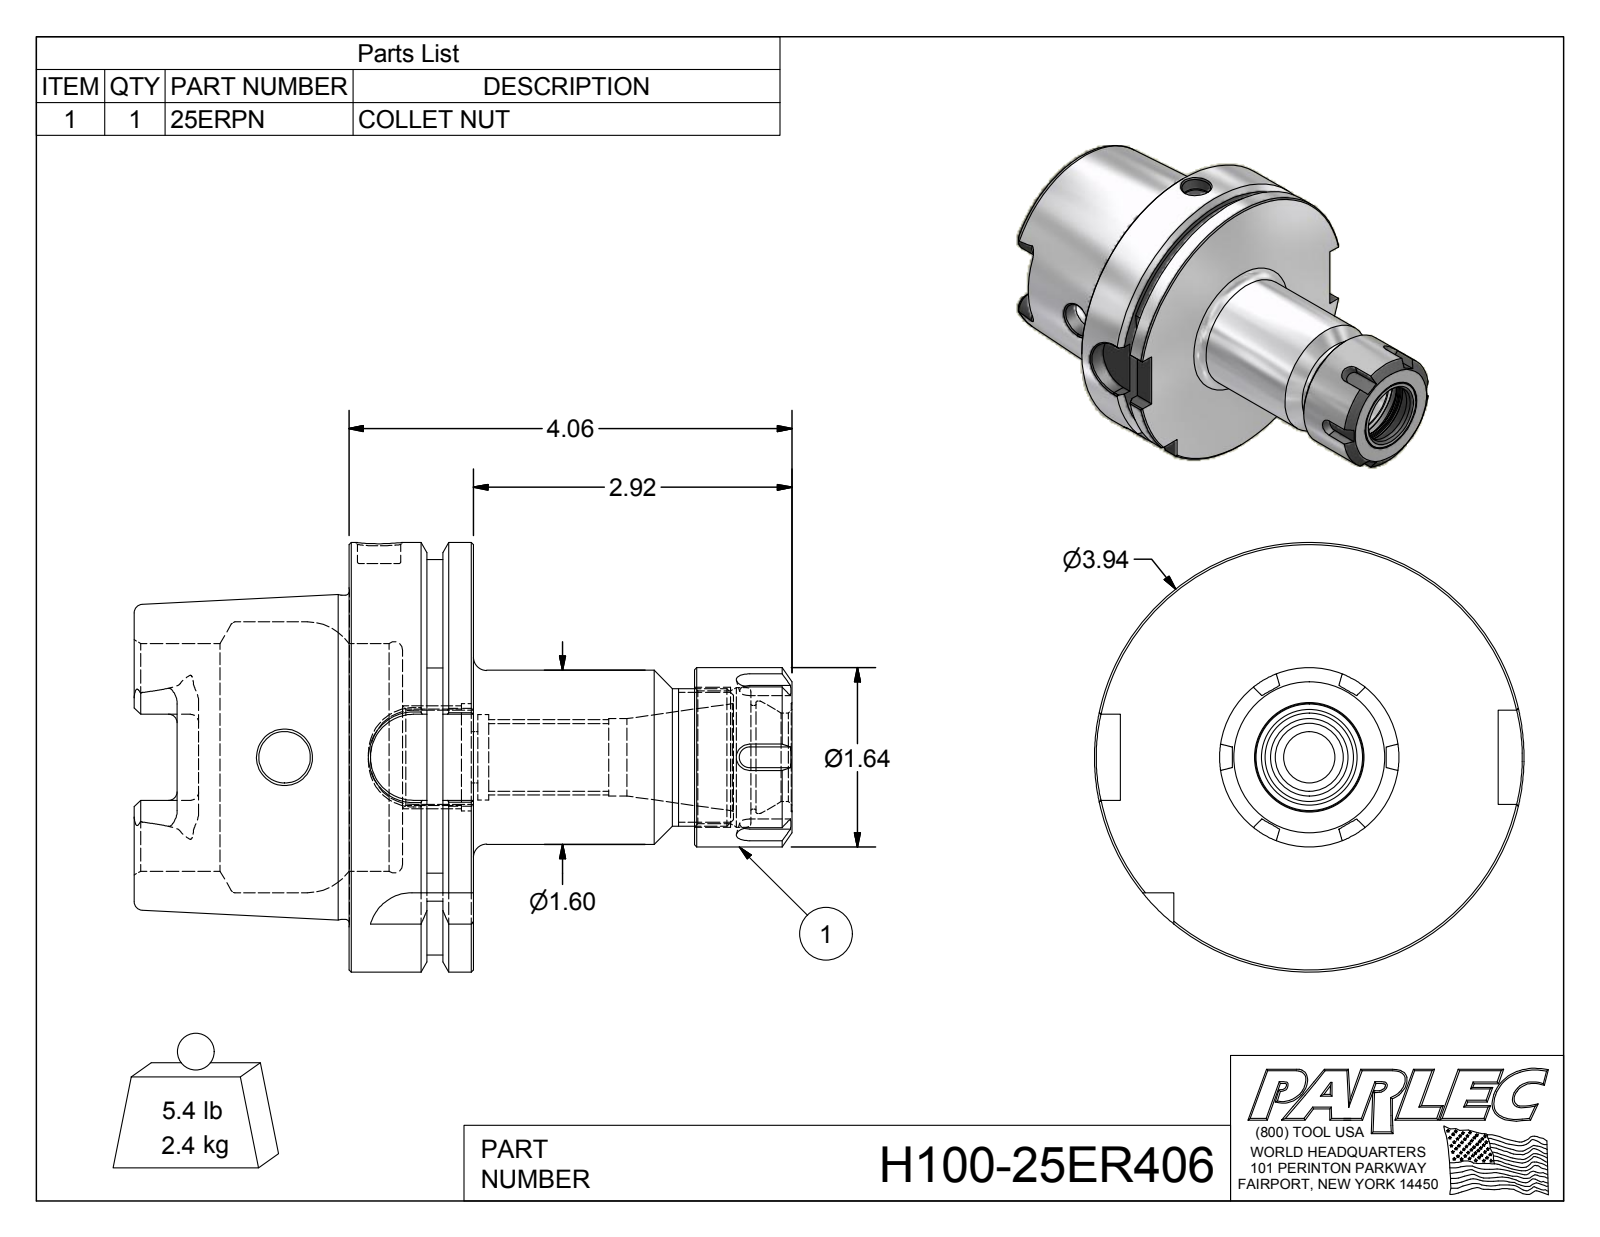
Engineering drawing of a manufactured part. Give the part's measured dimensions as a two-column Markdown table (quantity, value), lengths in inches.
| quantity | value |
| --- | --- |
| part name | H100-25ER406; H100-25ER4-1; 25ERPN |
| STEP written by | Autodesk Inventor 2012 (AUTOMOTIVE_DESIGN) |
| units | inches |
| bodies | 2 solids, 180 faces (69 planar, 43 cylindrical, 68 other) |
| overall size | 6.029 × 3.937 × 3.937 |
| volume | 19.69 in³ |
| surface area | 104.1 in² |
| round holes (diameter × count) | 0.472 × 2, 0.394 × 1, 0.472 × 1, 0.62 × 1, 0.71 × 1, 0.785 × 1, 0.811 × 1, 0.881 × 1, 0.95 × 1, 0.985 × 1, 1.027 × 1, 1.217 × 1 |
| round bosses / shafts (diameter × count) | 3.937 × 1, 2.967 × 1, 1.643 × 1, 1.595 × 1, 1.26 × 1 |
| partial cylindrical surfaces (radius × count) | 0.079 × 6, 0.192 × 4, 0.394 × 4, 1.811 × 1 |
| main face-to-face distances | 1.142, 0.492, 0.65, 1.969, 2.461, 3.11, 2.83, 0.861, 0.369, 0.281 |
